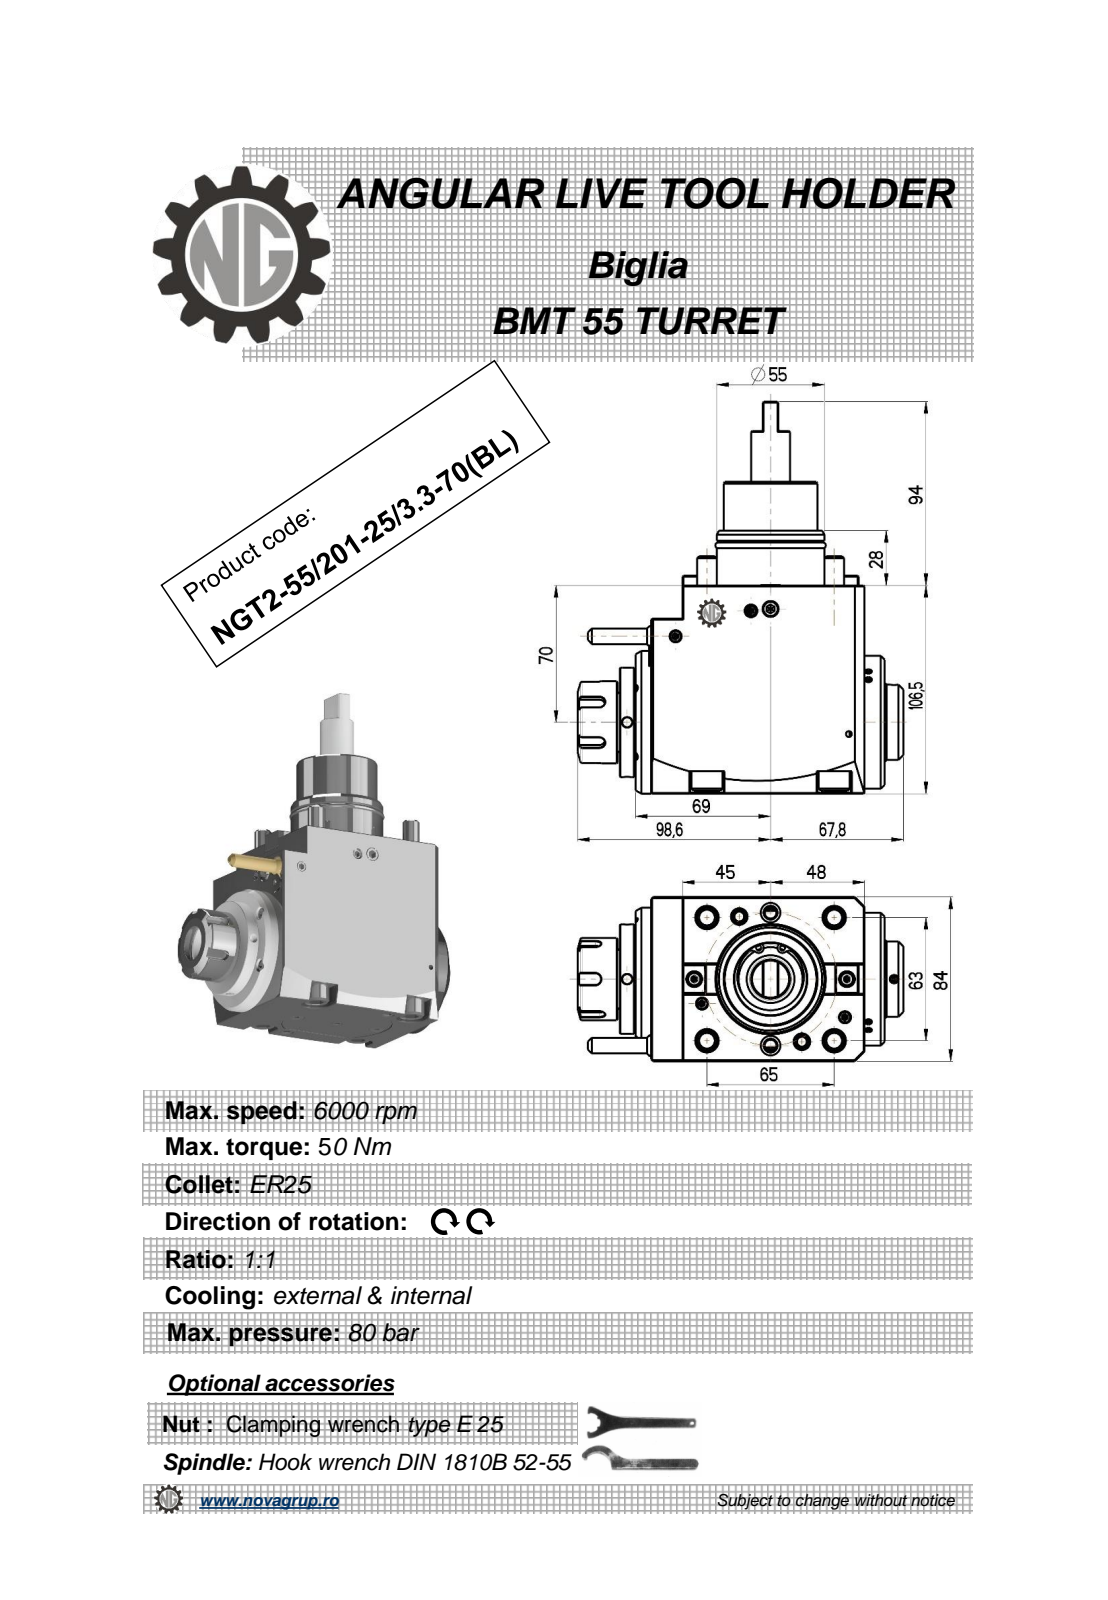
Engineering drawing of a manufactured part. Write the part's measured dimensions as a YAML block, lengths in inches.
part_name: "NGT2_55_201_25_3_3_70_BL"
step_written_by: "PRO/ENGINEER BY PARAMETRIC TECHNOLOGY CORPORATION, 2010280 (CONFIG_CONTROL_DESIGN)"
units: inches
bodies: {solids: 2, faces: 461, planar: 205, cylindrical: 114, other: 142}
overall_size: [7.894, 6.551, 3.307]
volume: 72.86
surface_area: 141.3
round_holes:
  - {diameter: 0.197, count: 3}
  - {diameter: 0.236, count: 2}
  - {diameter: 0.118, count: 1}
round_bosses_or_shafts:
  - {diameter: 0.63, count: 4}
  - {diameter: 0.394, count: 4}
  - {diameter: 2.874, count: 1}
  - {diameter: 2.677, count: 1}
  - {diameter: 2.205, count: 1}
  - {diameter: 2.165, count: 1}
  - {diameter: 1.969, count: 1}
  - {diameter: 1.89, count: 1}
partial_cylinders:
  - {radius: 0.013, count: 20}
  - {radius: 0.009, count: 6}
  - {radius: 0.118, count: 5}
  - {radius: 0.335, count: 4}
  - {radius: 0.031, count: 2}
  - {radius: 18.898, count: 2}
  - {radius: 0.134, count: 1}
  - {radius: 0.157, count: 1}
face_to_face_distances: [3.307, 4.193, 0.315, 4.291, 0.63, 4.606, 5.012, 4.697, 0.406, 0.669]
hole_center_spacings: [3.18, 2.677]
